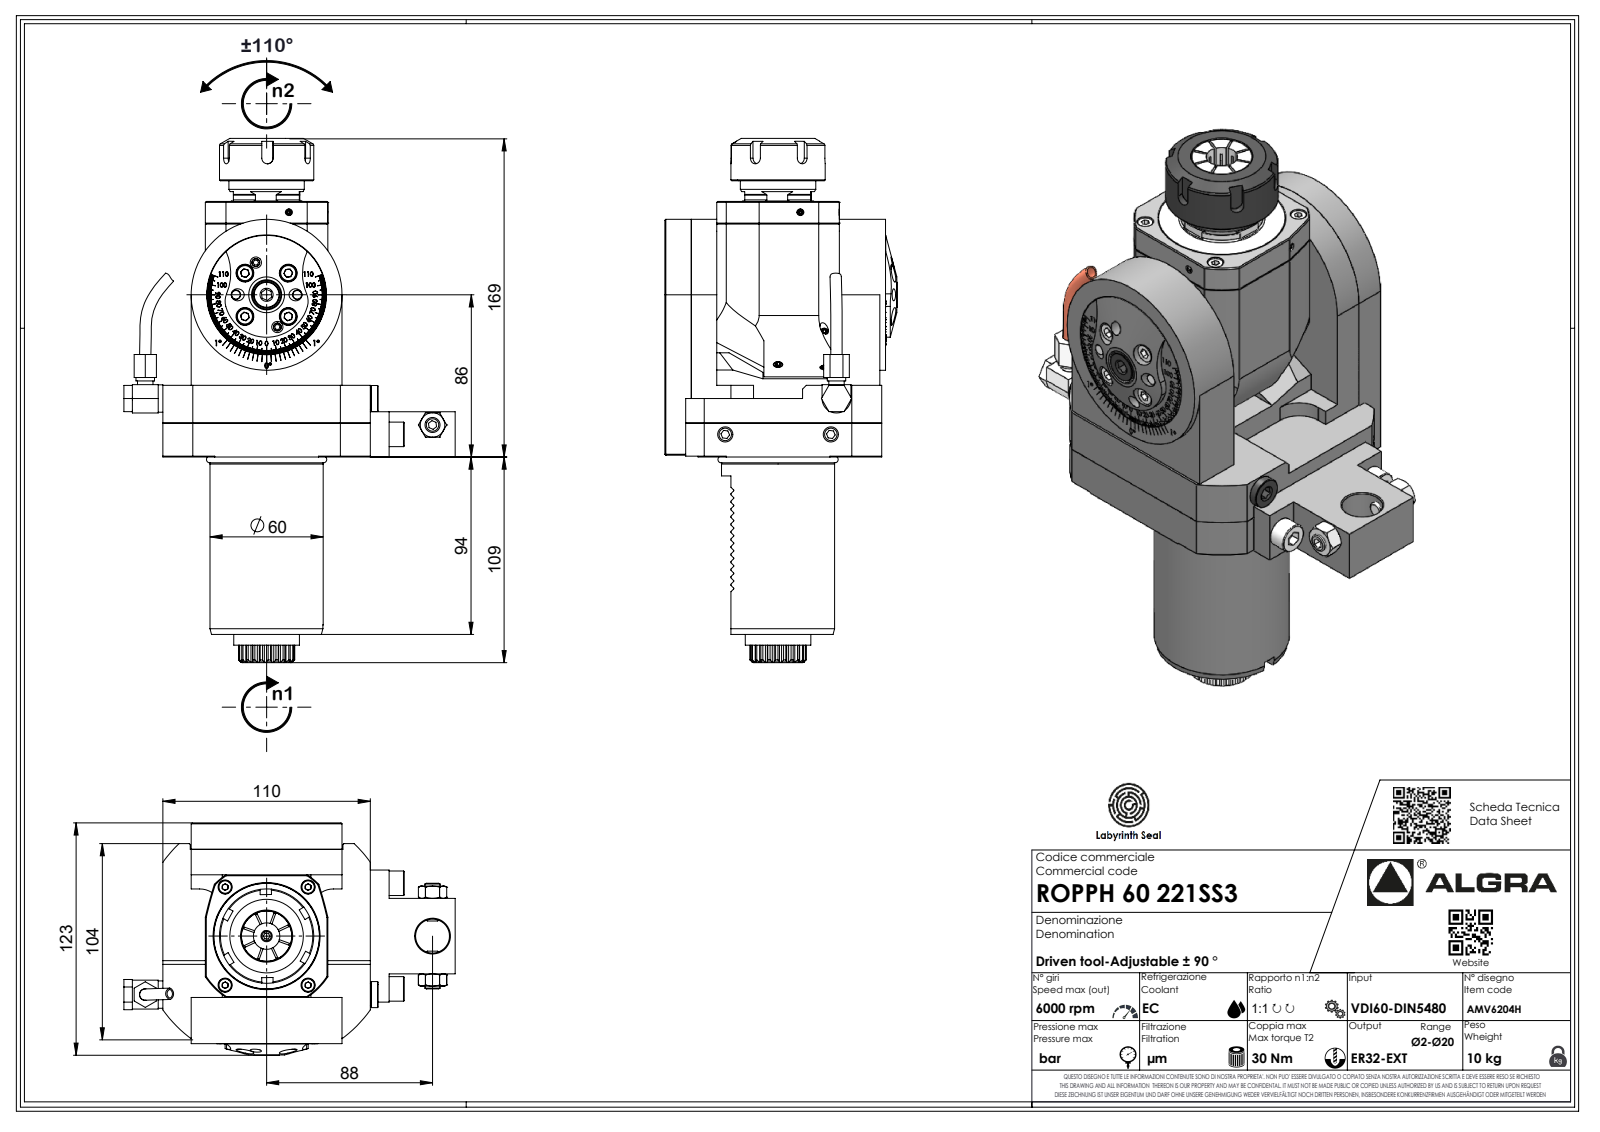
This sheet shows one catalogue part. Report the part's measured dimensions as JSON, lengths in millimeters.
{"part_name": "ROPPH60221SS3", "step_written_by": "SolidWorks 2023 (AUTOMOTIVE_DESIGN)", "units": "millimeters", "bodies": {"solids": 1, "faces": 922, "planar": 592, "cylindrical": 166, "other": 164}, "overall_size": [277.91, 175.7, 123], "volume_mm3": 1236000, "surface_area_mm2": 124065, "round_holes": [[2.1, 1], [50, 1]], "round_bosses_or_shafts": [[80, 1], [60, 1], [58.7, 1], [40, 1], [34.8, 1], [14.5, 1], [9.8, 1], [8.2, 1]], "partial_cylinders_radius": [[0.3, 14], [0.33, 7], [0.52, 7], [3.7, 7], [3, 5], [0.2, 3], [10, 2], [12, 2]], "face_to_face_distances": [22.5, 87.5, 65, 80, 7.5, 95, 15, 7, 135.5, 27.5]}
